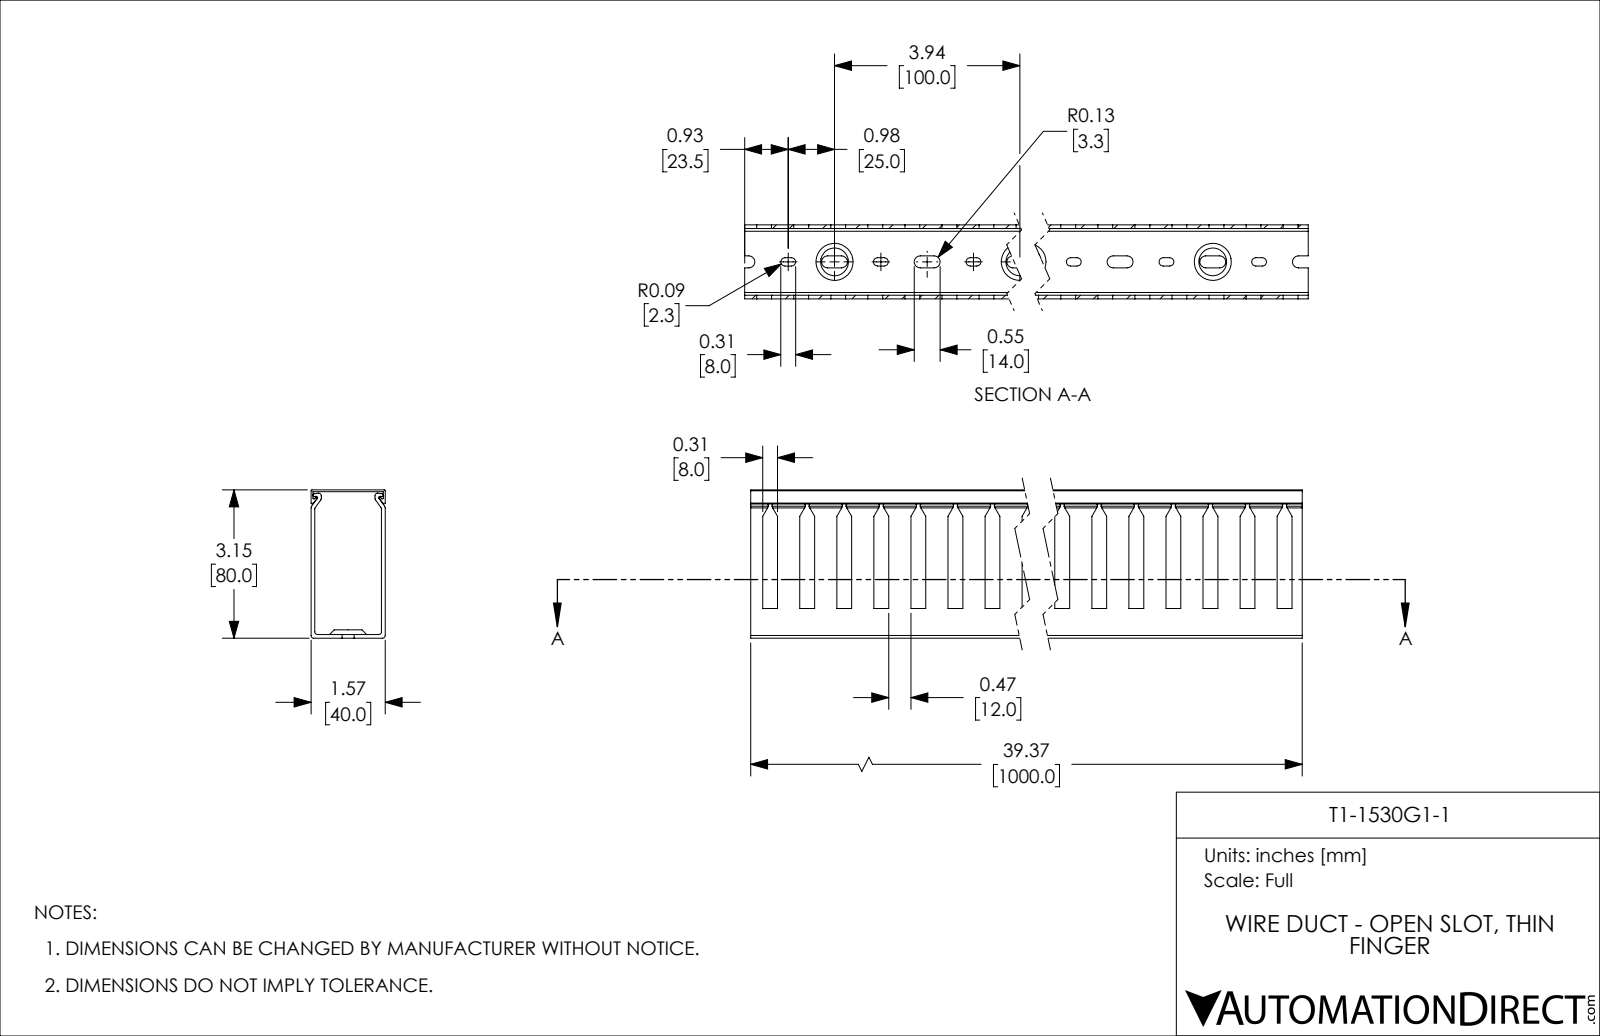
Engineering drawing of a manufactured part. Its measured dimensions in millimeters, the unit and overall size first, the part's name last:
Units: millimetres
Overall size (bounding box): 1000 × 80 × 40
Partial cylindrical surfaces — rounded edges, fillets, slot ends (radius × count): R2.25 ×40, R3.25 ×40, R1.5 ×12, R0.5 ×8, R0.75 ×6
Main face-to-face distances: 2, 38, 40, 36, 1, 80, 79, 77, 78, 39
Volume: 435 701 mm³ · Surface area: 497 843 mm²
Bodies: 2 solids, 775 faces (444 planar, 311 cylindrical, 20 other)
Part name (STEP PRODUCT): T1-1530G1-1
STEP written by: SolidWorks 2021 (CONFIG_CONTROL_DESIGN)
